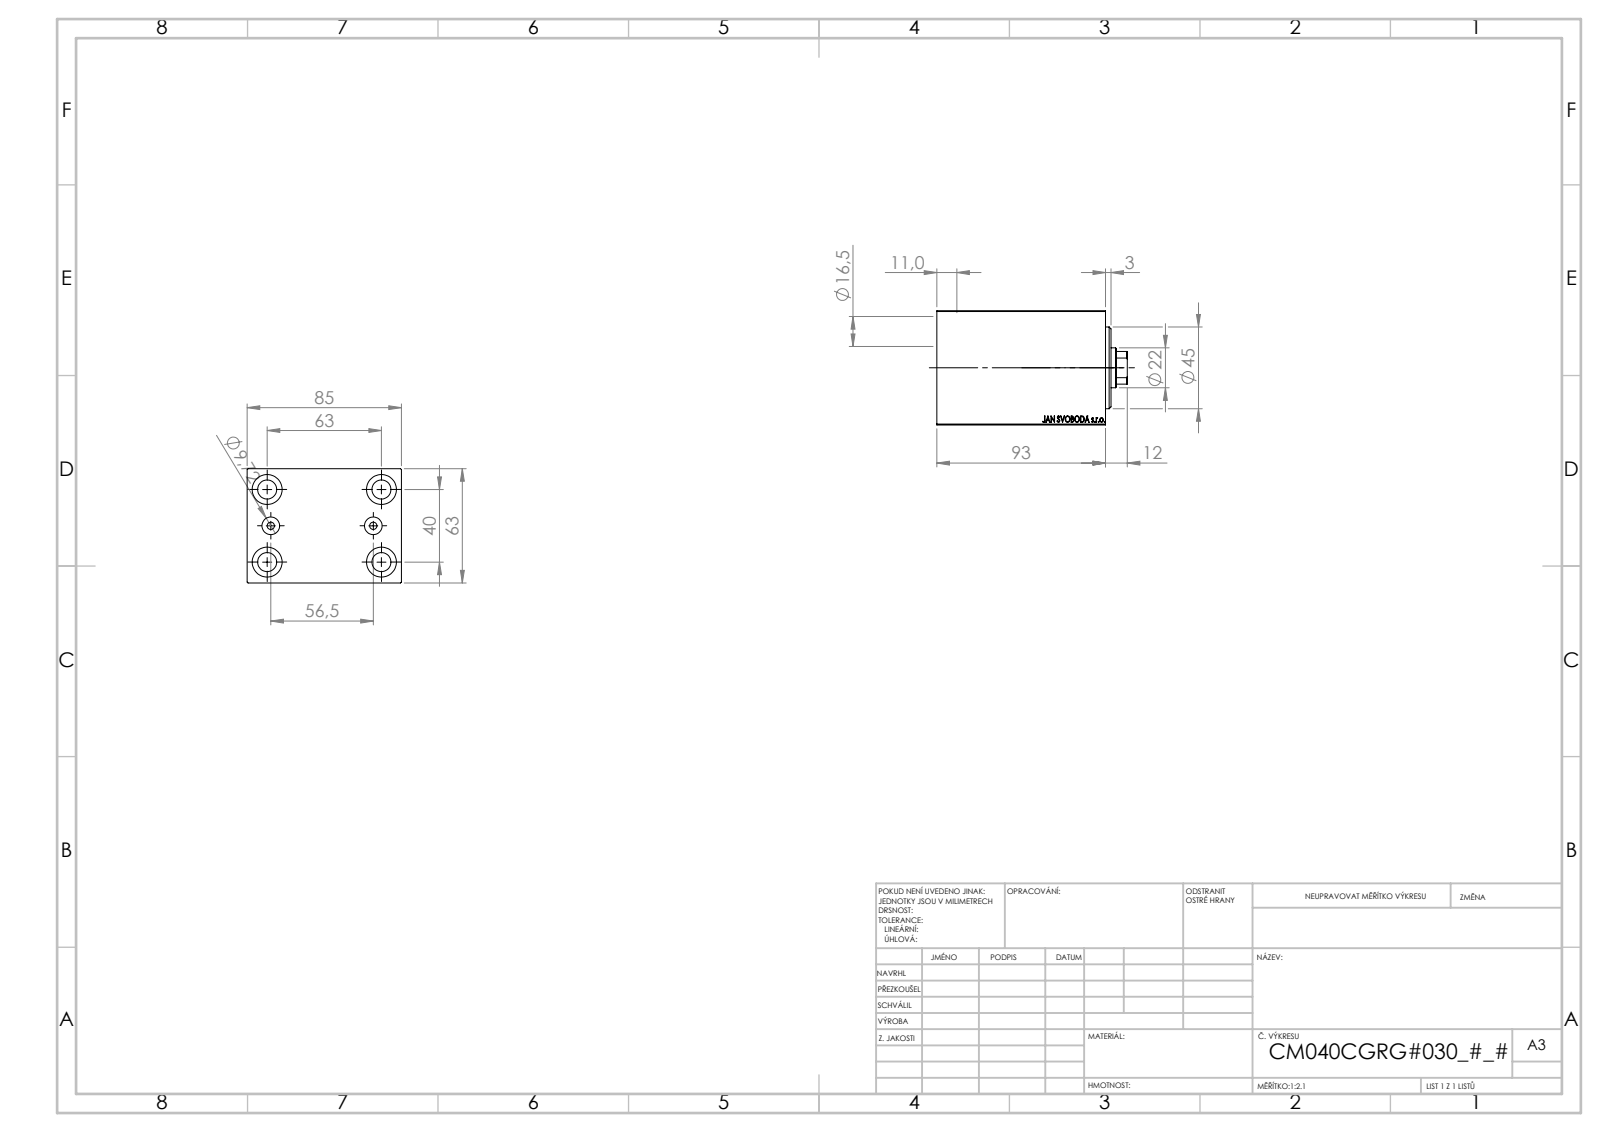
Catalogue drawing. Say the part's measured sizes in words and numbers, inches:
The part is named "V450CM_C_Body; V450CM_C_VCP; V450CM_VC_B". Its 3-D file was written by "SolidWorks 2019 (CONFIG_CONTROL_DESIGN)". It is 3 solids with 858 faces: 408 planar, 56 cylindrical and 394 other. Overall it measures 4.134 by 3.346 by 2.48 inches. Its volume is 26.22 cubic inches and its surface area 126.5 square inches. Round holes: 4 of diameter 0.413, 4 of diameter 0.65, 2 of diameter 0.157, 2 of diameter 0.383, 1 of diameter 0.492, 1 of diameter 0.866, 1 of diameter 1.004, 1 of diameter 1.575, 1 of diameter 1.654, 1 of diameter 1.772. Partial cylindrical surfaces (rounded edges, fillets, slot ends): 1 of radius 0.413. The main face-to-face distances are 2.48, 3.346, 0.472, 3.189, 3.661, 0.039, 2.717, 0.433, 3.228, 2.756. The hole center spacings are 1.469, 0.791, 0.807, 1.575, 2.434, 2.48, 2.528, 2.938.
